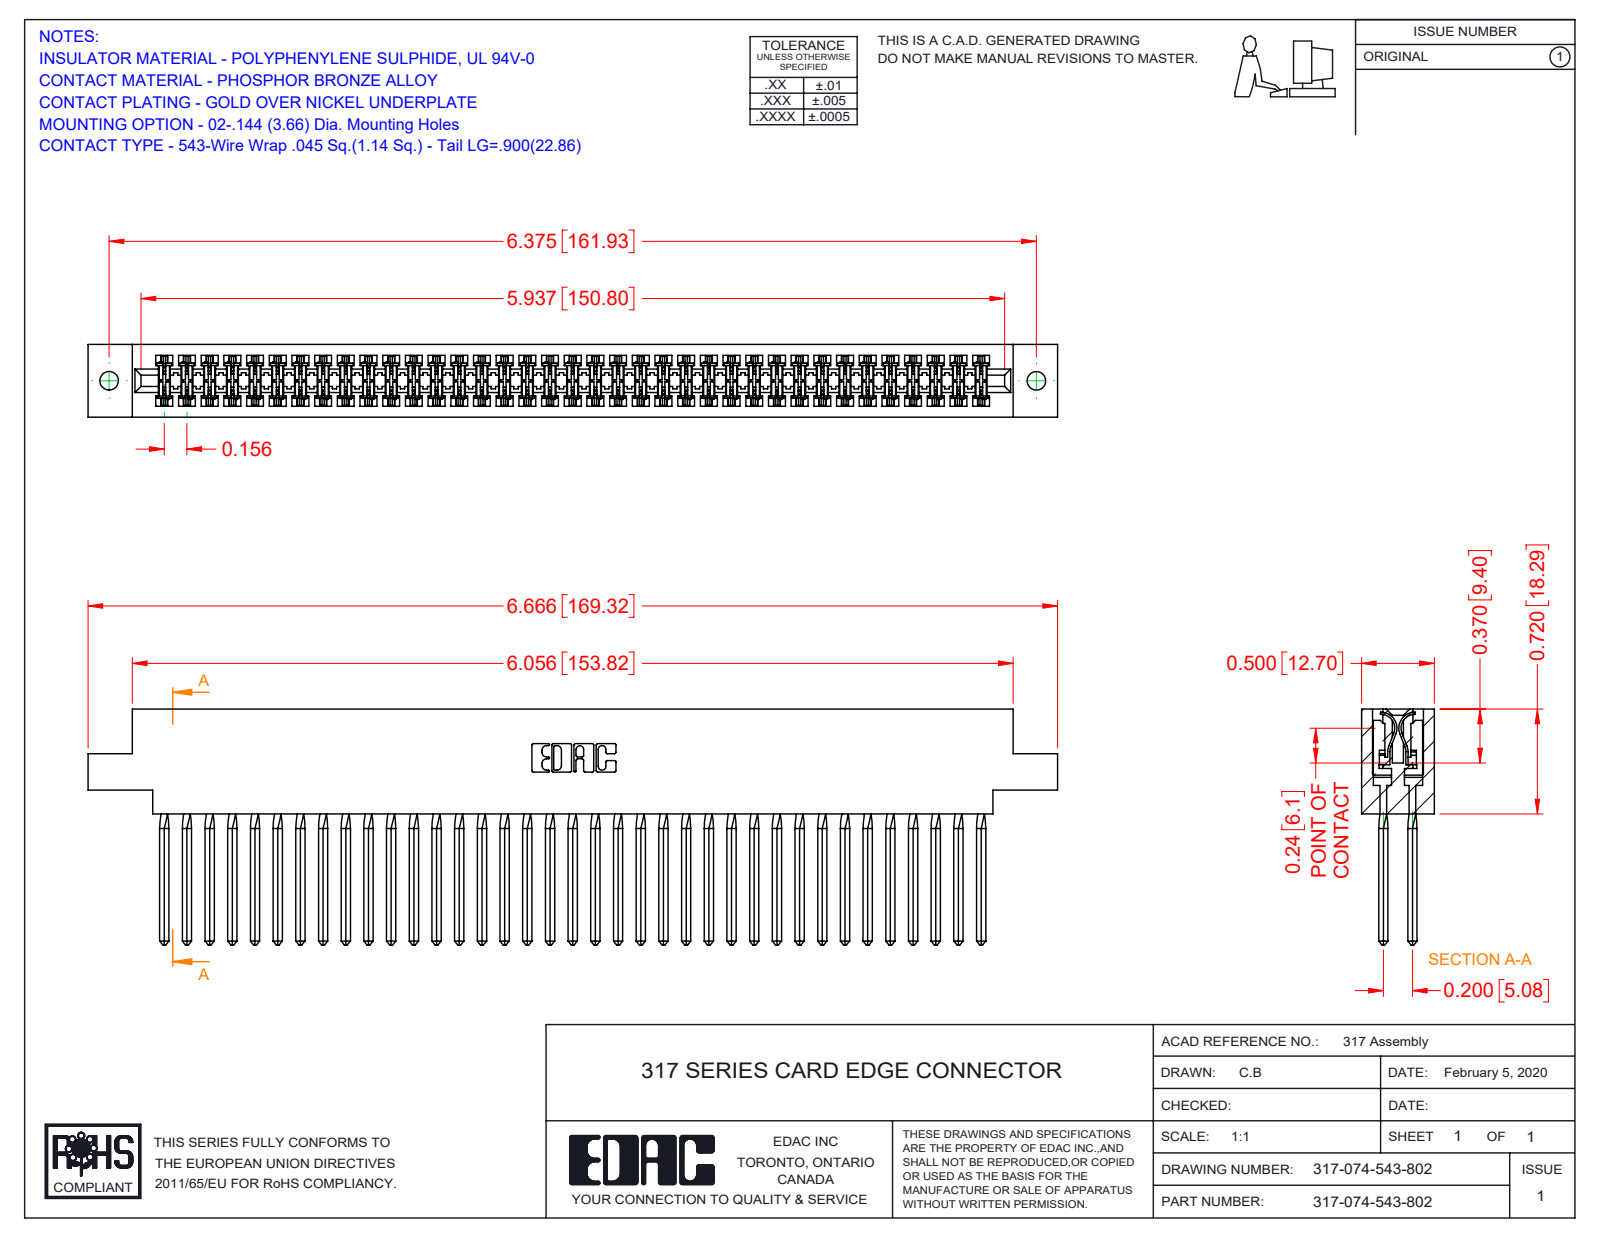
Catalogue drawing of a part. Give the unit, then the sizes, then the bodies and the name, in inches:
Units: inches
Overall size (bounding box): 6.666 × 1.62 × 0.5
Round holes (diameter × count): ⌀0.128 ×2
Partial cylindrical surfaces — rounded edges, fillets, slot ends (radius × count): R0.015 ×148, R0.01 ×22, R0.007 ×6, R0.031 ×6, R0.026 ×3, R0.095 ×2, R0.1 ×2, R0.11 ×2
Main face-to-face distances: 0.5, 0.075, 0.425, 0.35, 0.11, 0.195, 0.094, 0.2, 0.115, 0.131
Hole centre spacings: 6.375
Volume: 1.744 in³ · Surface area: 66.49 in²
Bodies: 75 solids, 6688 faces (5460 planar, 932 cylindrical, 296 other)
Part name (STEP PRODUCT): 317-074-543-802; 317-290-001_543; 317 Part_.144 Dia
STEP written by: SolidWorks 2016 (CONFIG_CONTROL_DESIGN)
